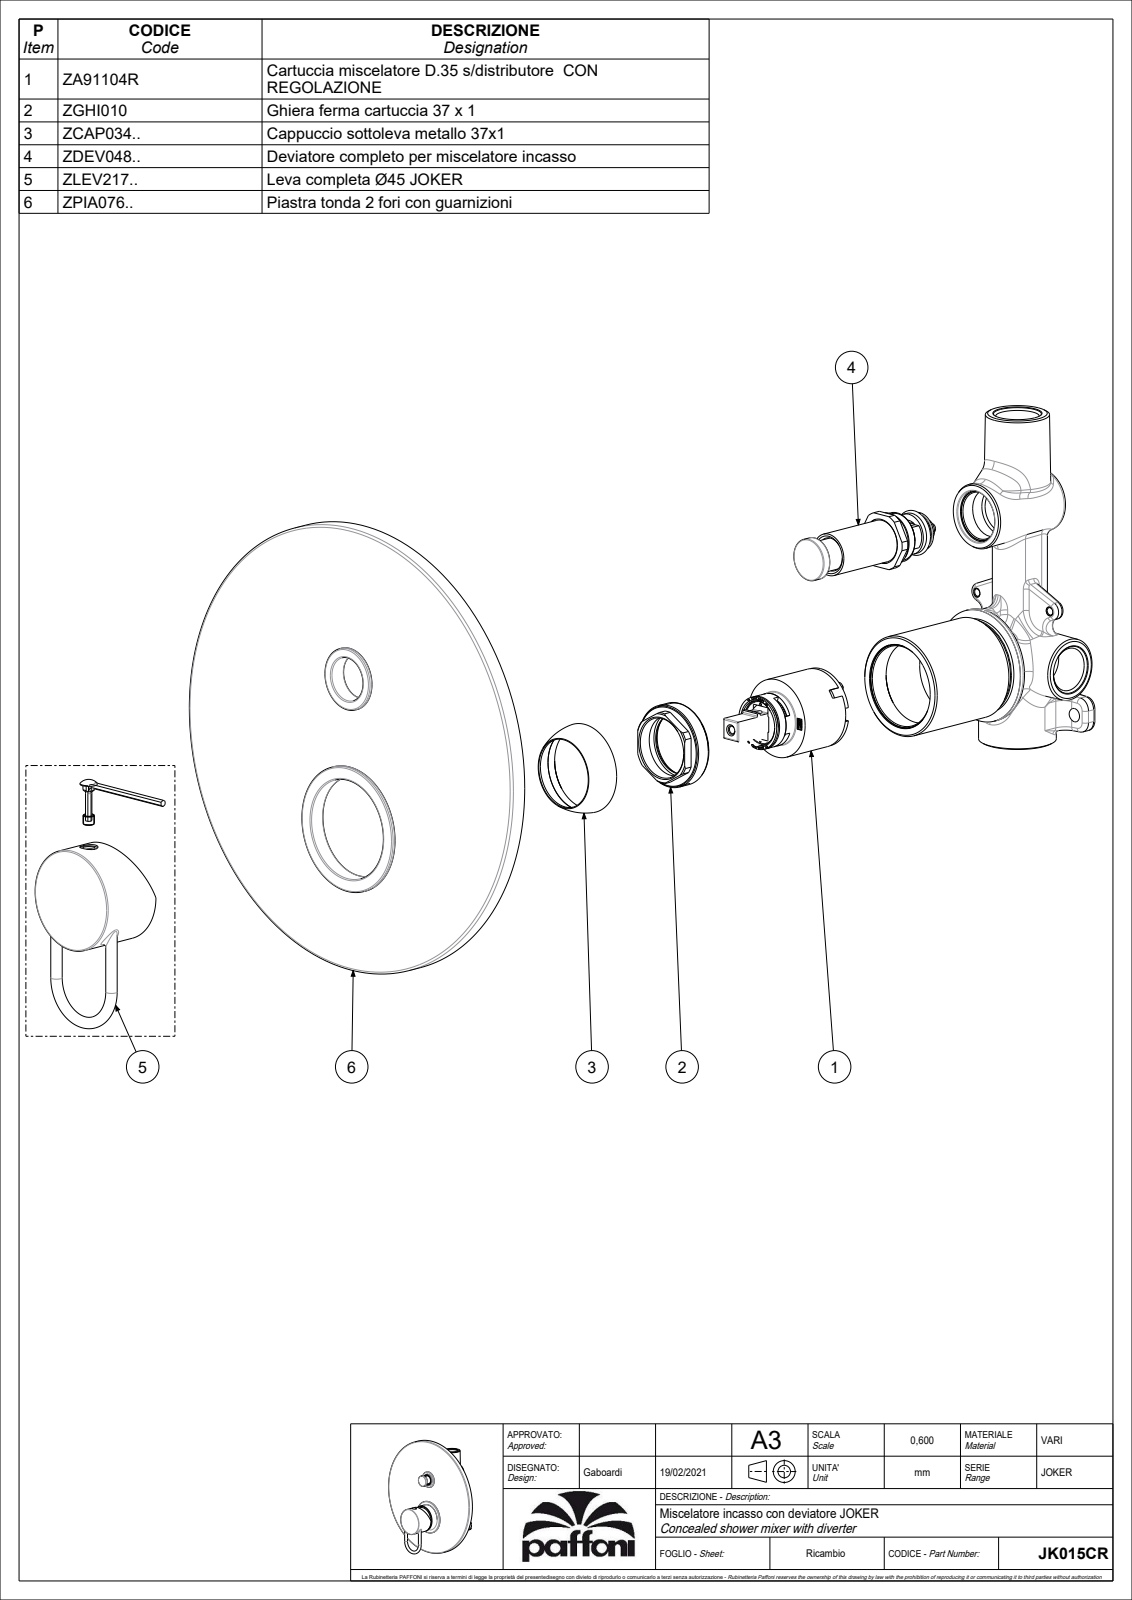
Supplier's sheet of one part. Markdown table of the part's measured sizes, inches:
| quantity | value |
| --- | --- |
| part name | JK015CR |
| STEP written by | CREO PARAMETRIC BY PTC INC, 2020044 (CONFIG_CONTROL_DESIGN) |
| units | inches |
| bodies | 2 solids, 147 faces (42 planar, 48 cylindrical, 57 other) |
| overall size | 7.874 × 7.874 × 2.185 |
| volume | 17.35 in³ |
| surface area | 136.9 in² |
| round holes (diameter × count) | 0.118 × 1, 0.165 × 1, 0.217 × 1, 1.205 × 1, 1.417 × 1, 1.476 × 1 |
| round bosses / shafts (diameter × count) | 0.197 × 2, 7.874 × 1, 2.213 × 1, 1.772 × 1, 1.764 × 1, 1.091 × 1, 0.736 × 1, 0.732 × 1 |
| partial cylindrical surfaces (radius × count) | 0.061 × 2 |
| main face-to-face distances | 0.315, 0.079, 0.394, 1.697, 2.012, 1.618, 0.512, 0.906, 0.591, 1.106 |
